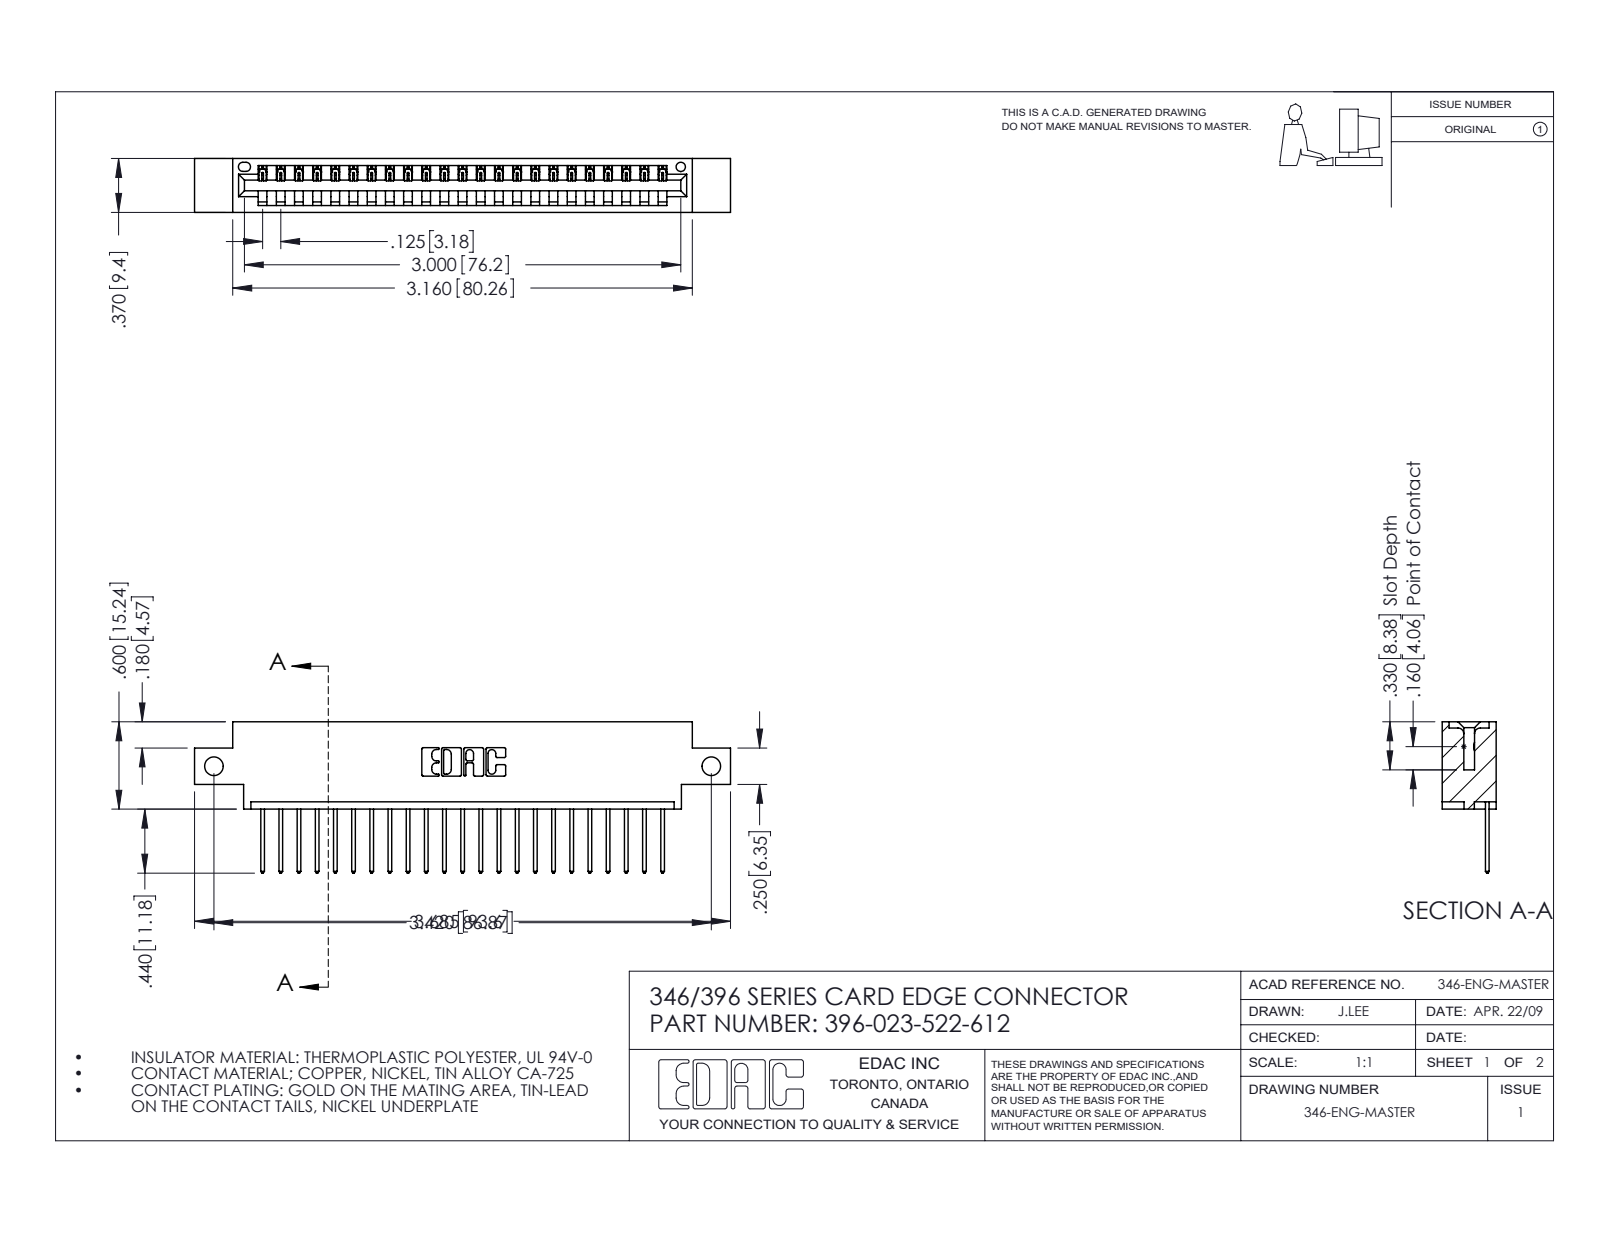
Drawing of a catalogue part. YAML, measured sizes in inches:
part_name: "346 Part_0.170 Offset - Side Mount; 396-023-522-612; 345-292-001_345-293-122"
step_written_by: "SolidWorks 2016 (CONFIG_CONTROL_DESIGN)"
units: inches
bodies: {solids: 24, faces: 1460, planar: 1000, cylindrical: 460, other: 0}
overall_size: [3.685, 1.04, 0.37]
volume: 0.524
surface_area: 16.48
round_holes:
  - {diameter: 0.128, count: 2}
  - {diameter: 0.064, count: 1}
partial_cylinders:
  - {radius: 0.006, count: 46}
  - {radius: 0.01, count: 46}
  - {radius: 0.01, count: 22}
  - {radius: 0.007, count: 6}
  - {radius: 0.031, count: 6}
  - {radius: 0.026, count: 3}
  - {radius: 0.031, count: 2}
  - {radius: 0.04, count: 2}
face_to_face_distances: [0.048, 0.322, 0.37, 0.25, 0.072, 0.298, 0.025, 0.148, 0.222, 0.1]
hole_center_spacings: [3.42]
